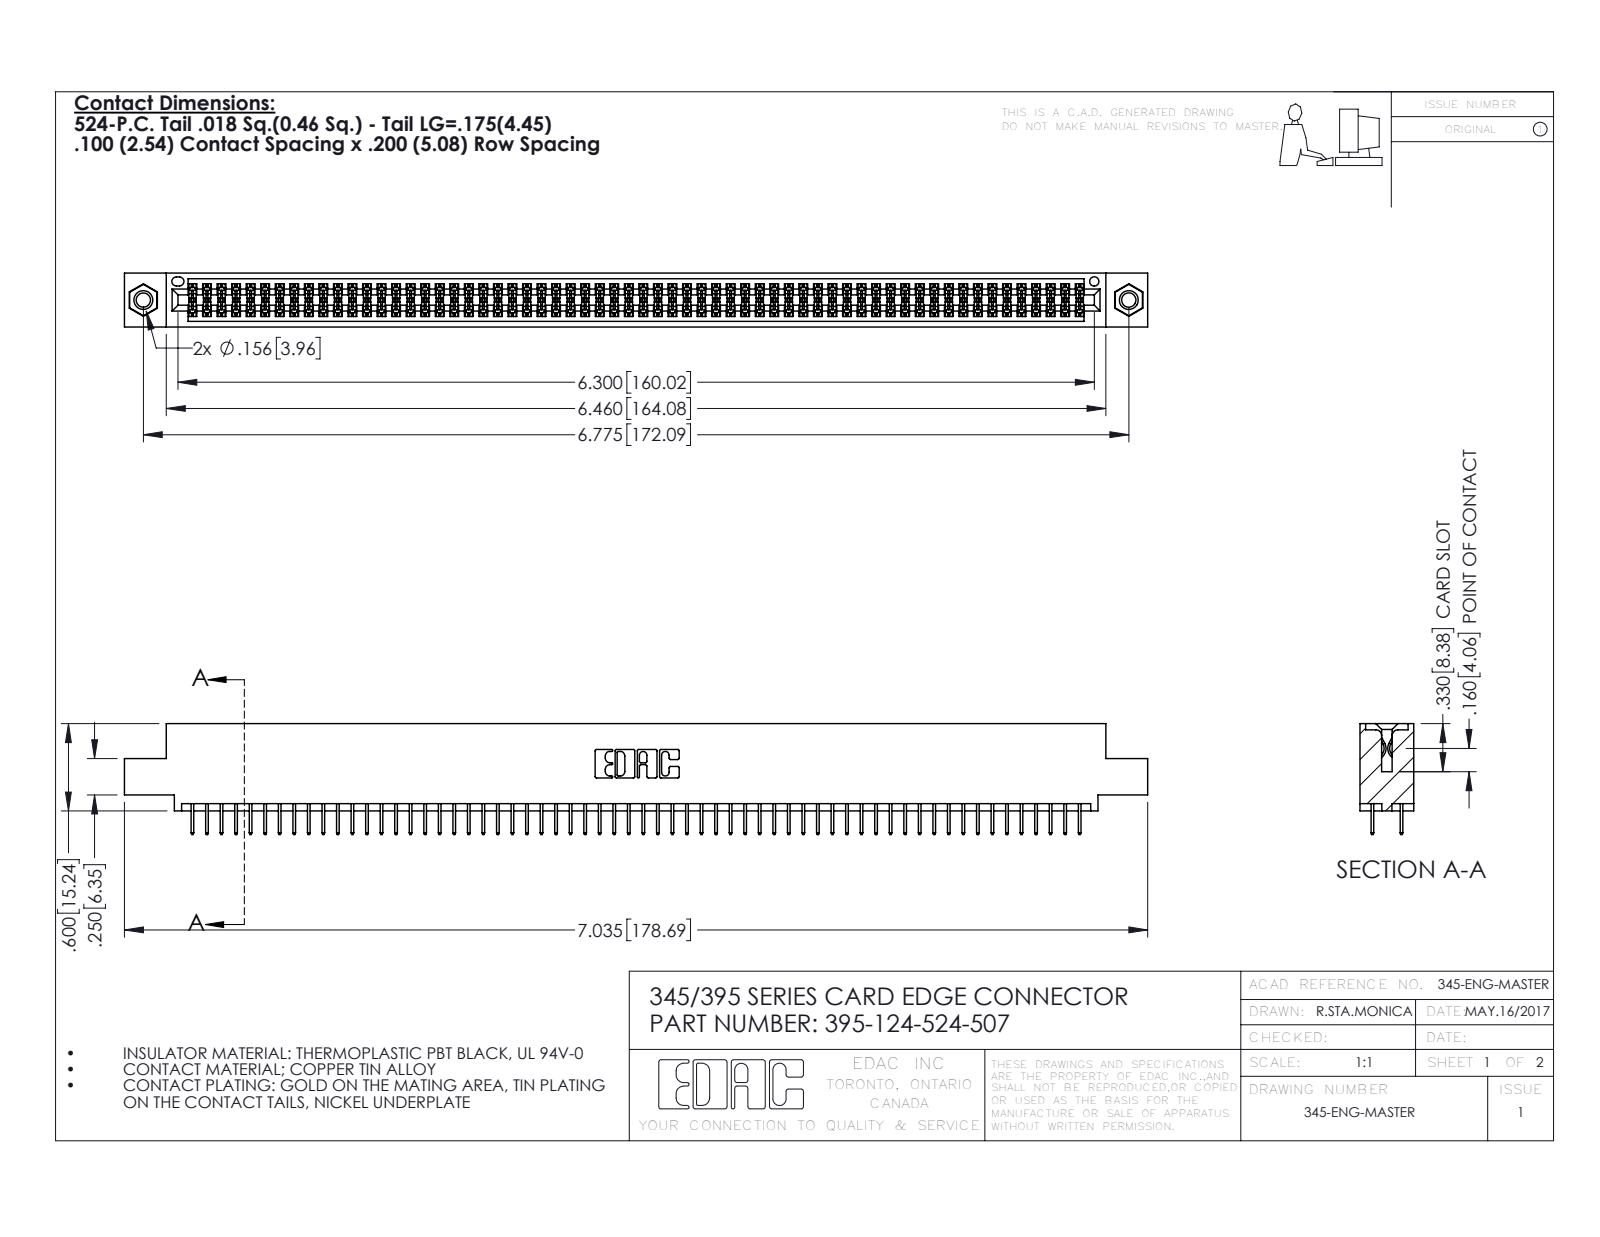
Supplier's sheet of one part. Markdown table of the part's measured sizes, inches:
| quantity | value |
| --- | --- |
| part name | 345-250-001_345-250-005-103; 345-292-001_345-293-124; 395-124-524-507; 345 Part_0.110 Offset - 0.156 Dia-TI |
| STEP written by | SolidWorks 2016 (CONFIG_CONTROL_DESIGN) |
| units | inches |
| bodies | 127 solids, 6886 faces (4952 planar, 1918 cylindrical, 16 other) |
| overall size | 7.035 × 0.762 × 0.37 |
| volume | 1.054 in³ |
| surface area | 39.59 in² |
| round holes (diameter × count) | 0.098 × 2, 0.125 × 2, 0.156 × 2, 0.064 × 1 |
| round bosses / shafts (diameter × count) | 0.155 × 2 |
| partial cylindrical surfaces (radius × count) | 0.006 × 186, 0.01 × 22, 0.007 × 6, 0.031 × 6, 0.026 × 3, 0.014 × 2, 0.019 × 2, 0.022 × 2 |
| main face-to-face distances | 0.072, 0.298, 0.2, 0.37, 0.098, 0.272, 0.025, 0.225, 0.072, 0.175 |
| hole center spacings | 0.27, 6.539, 6.775 |
